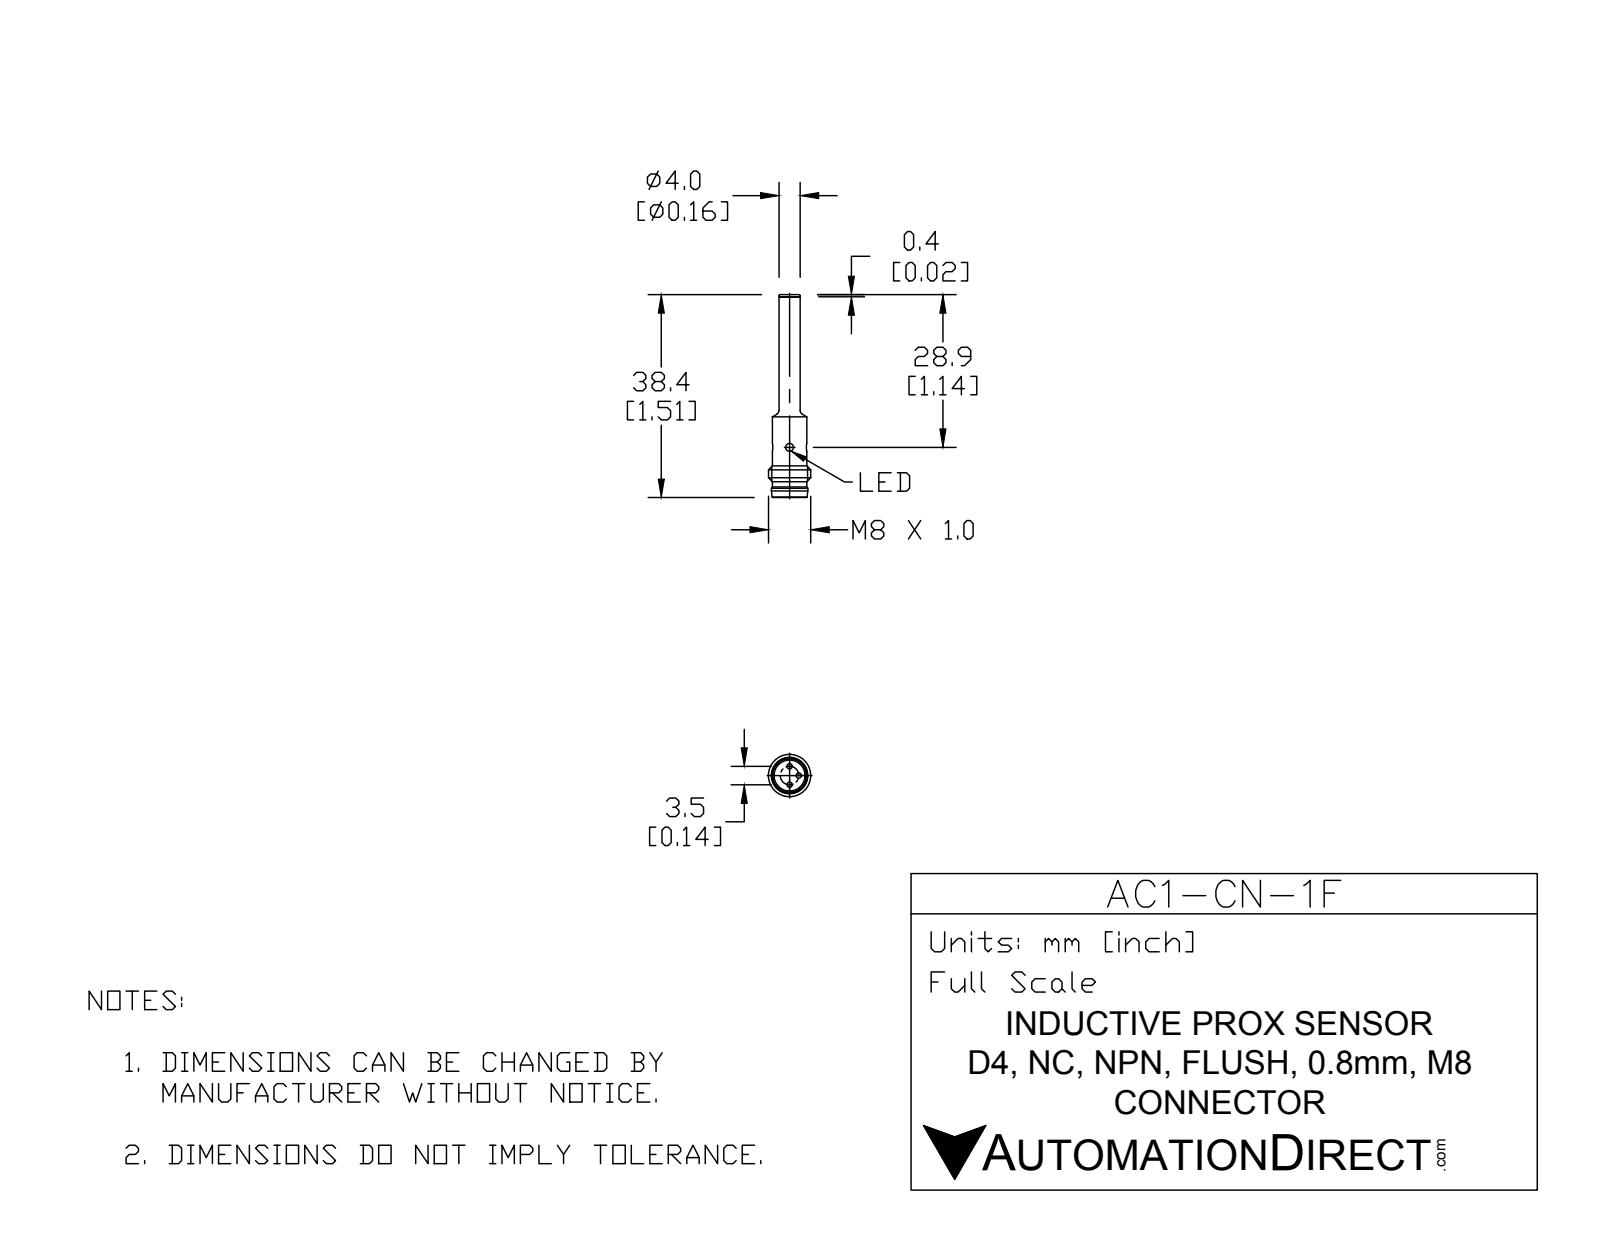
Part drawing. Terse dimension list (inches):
name: AC1-CN-1F
written by: SolidWorks 2015 (CONFIG_CONTROL_DESIGN)
unit: in
bodies: 4 solids, 59 faces (11 planar, 26 cylindrical, 22 other)
size: 1.512 × 0.315 × 0.315
volume: 0.046 in³; area: 1.3 in²
holes: 2× ⌀0.059, 1× ⌀0.23
bosses: 3× ⌀0.039, 1× ⌀0.315, 1× ⌀0.272, 1× ⌀0.256, 1× ⌀0.157
face distances: 1.315, 0.217, 0.197, 1.512, 1.496, 1.299, 0.016
